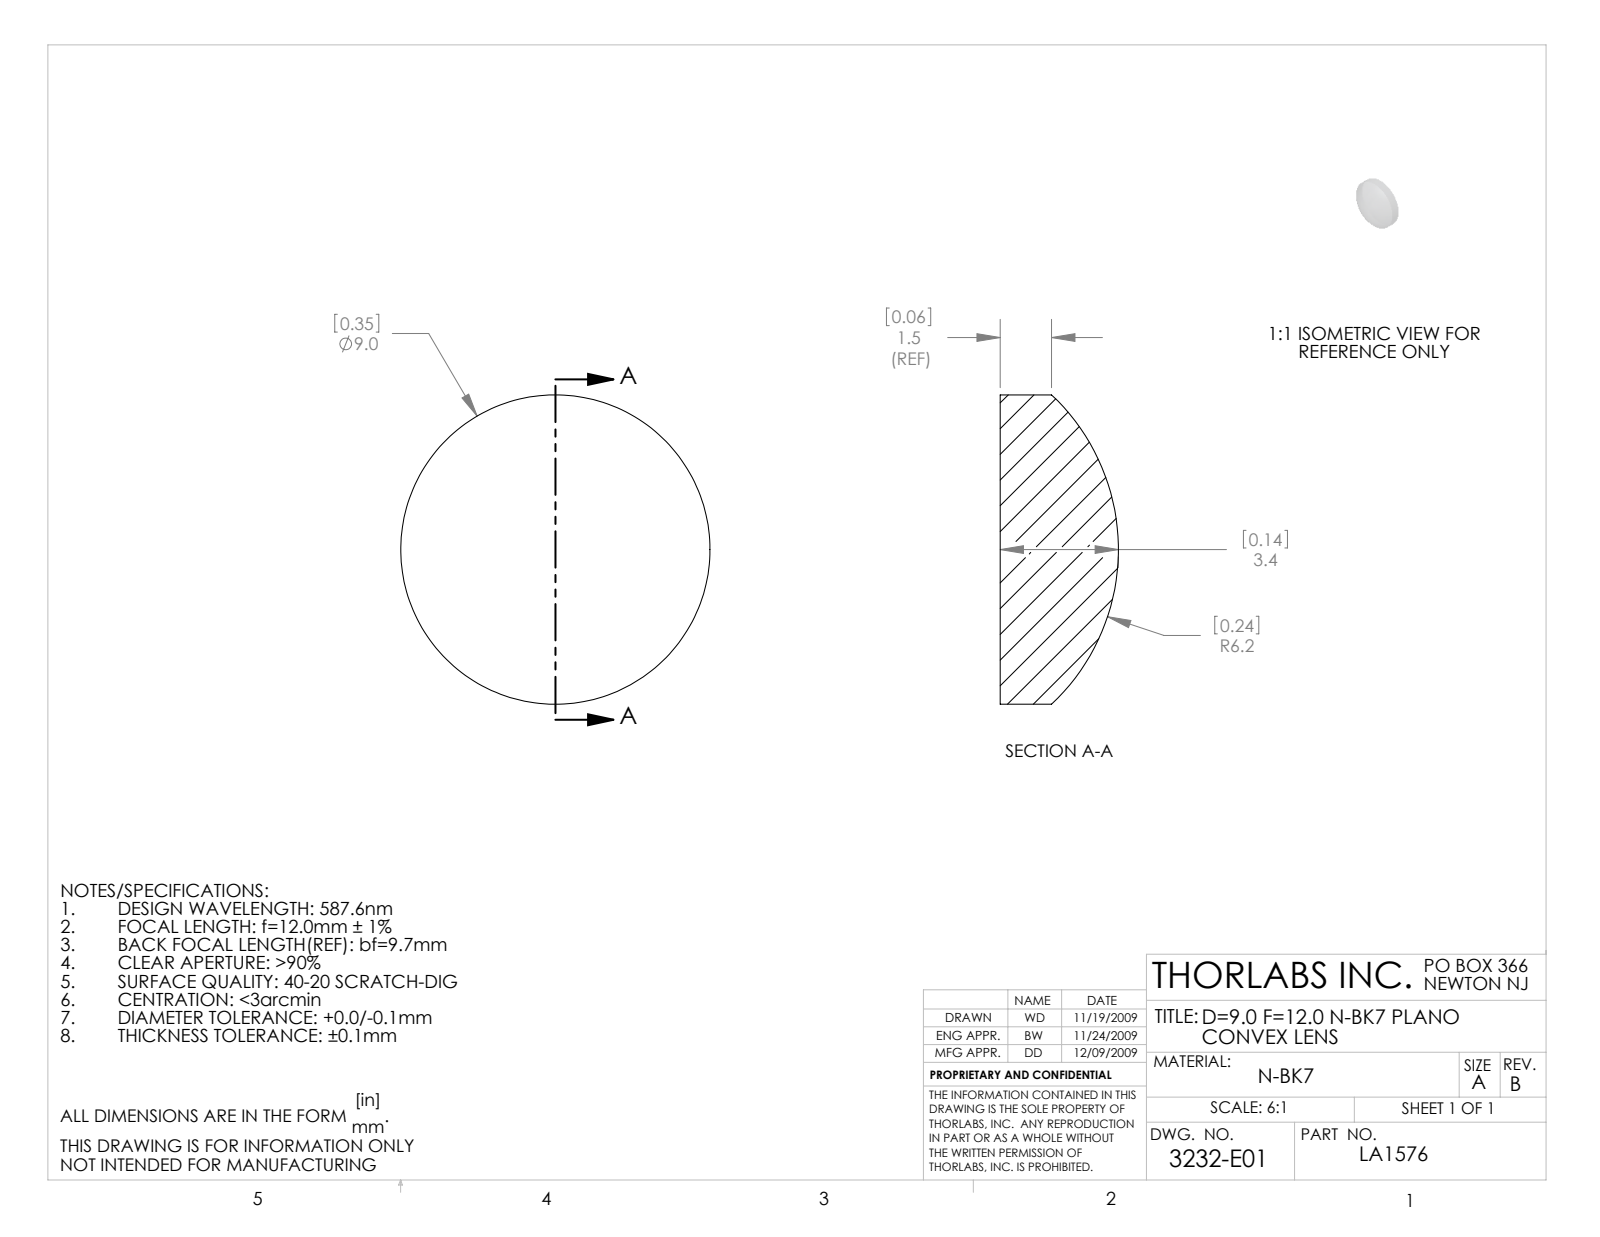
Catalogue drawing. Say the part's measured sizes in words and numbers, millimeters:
The part is named "3232-E0W". Its 3-D file was written by "SolidWorks 2009 (AUTOMOTIVE_DESIGN)". It is 1 solid with 5 faces: 1 planar, 2 cylindrical and 2 other. Overall it measures 9 by 9 by 3.44 millimeters. Its volume is 161 cubic millimeters and its surface area 181 square millimeters. Round bosses or shafts: 1 of diameter 9.
